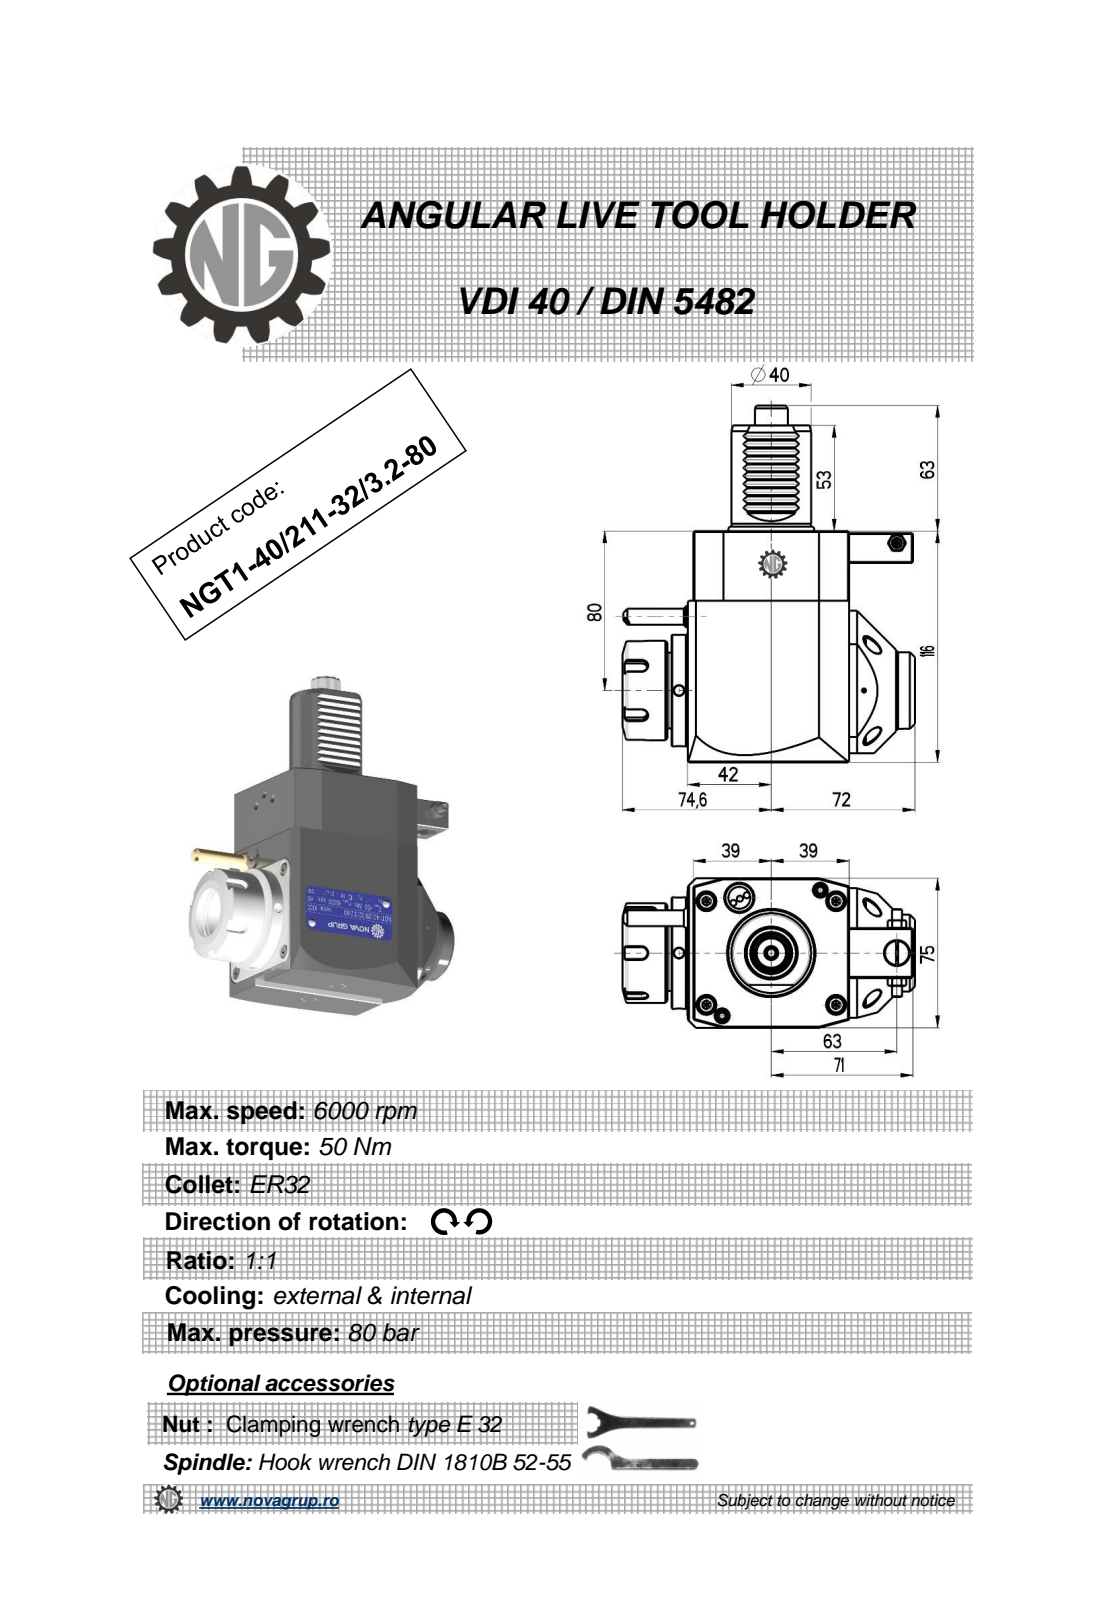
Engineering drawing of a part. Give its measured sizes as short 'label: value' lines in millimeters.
name: NGT1_40_211_32_3_2_80
written by: PRO/ENGINEER BY PARAMETRIC TECHNOLOGY CORPORATION, 2010280 (CONFIG_CONTROL_DESIGN)
unit: mm
bodies: 1 solid, 461 faces (183 planar, 124 cylindrical, 154 other)
size: 179 × 146.6 × 75
volume: 900 796 mm³; area: 72 210 mm²
holes: 3× ⌀5, 2× ⌀4.2, 1× ⌀3, 1× ⌀5.3, 1× ⌀9.5, 1× ⌀12, 1× ⌀27
bosses: 1× ⌀56, 1× ⌀50, 1× ⌀43, 1× ⌀40, 1× ⌀38.5, 1× ⌀11.2, 1× ⌀8.96, 1× ⌀8
rounds: 18× R3.03, 12× R0.26, 10× R0.3, 6× R0.22, 5× R3, 1× R0.5, 1× R6.75, 1× R8.25
face distances: 75, 116, 81, 78, 3, 111, 2.8, 80.8, 7.5, 0.5
hole spacings: 39.58, 40.93, 46.25, 63, 72.5, 109.25, 131.95
